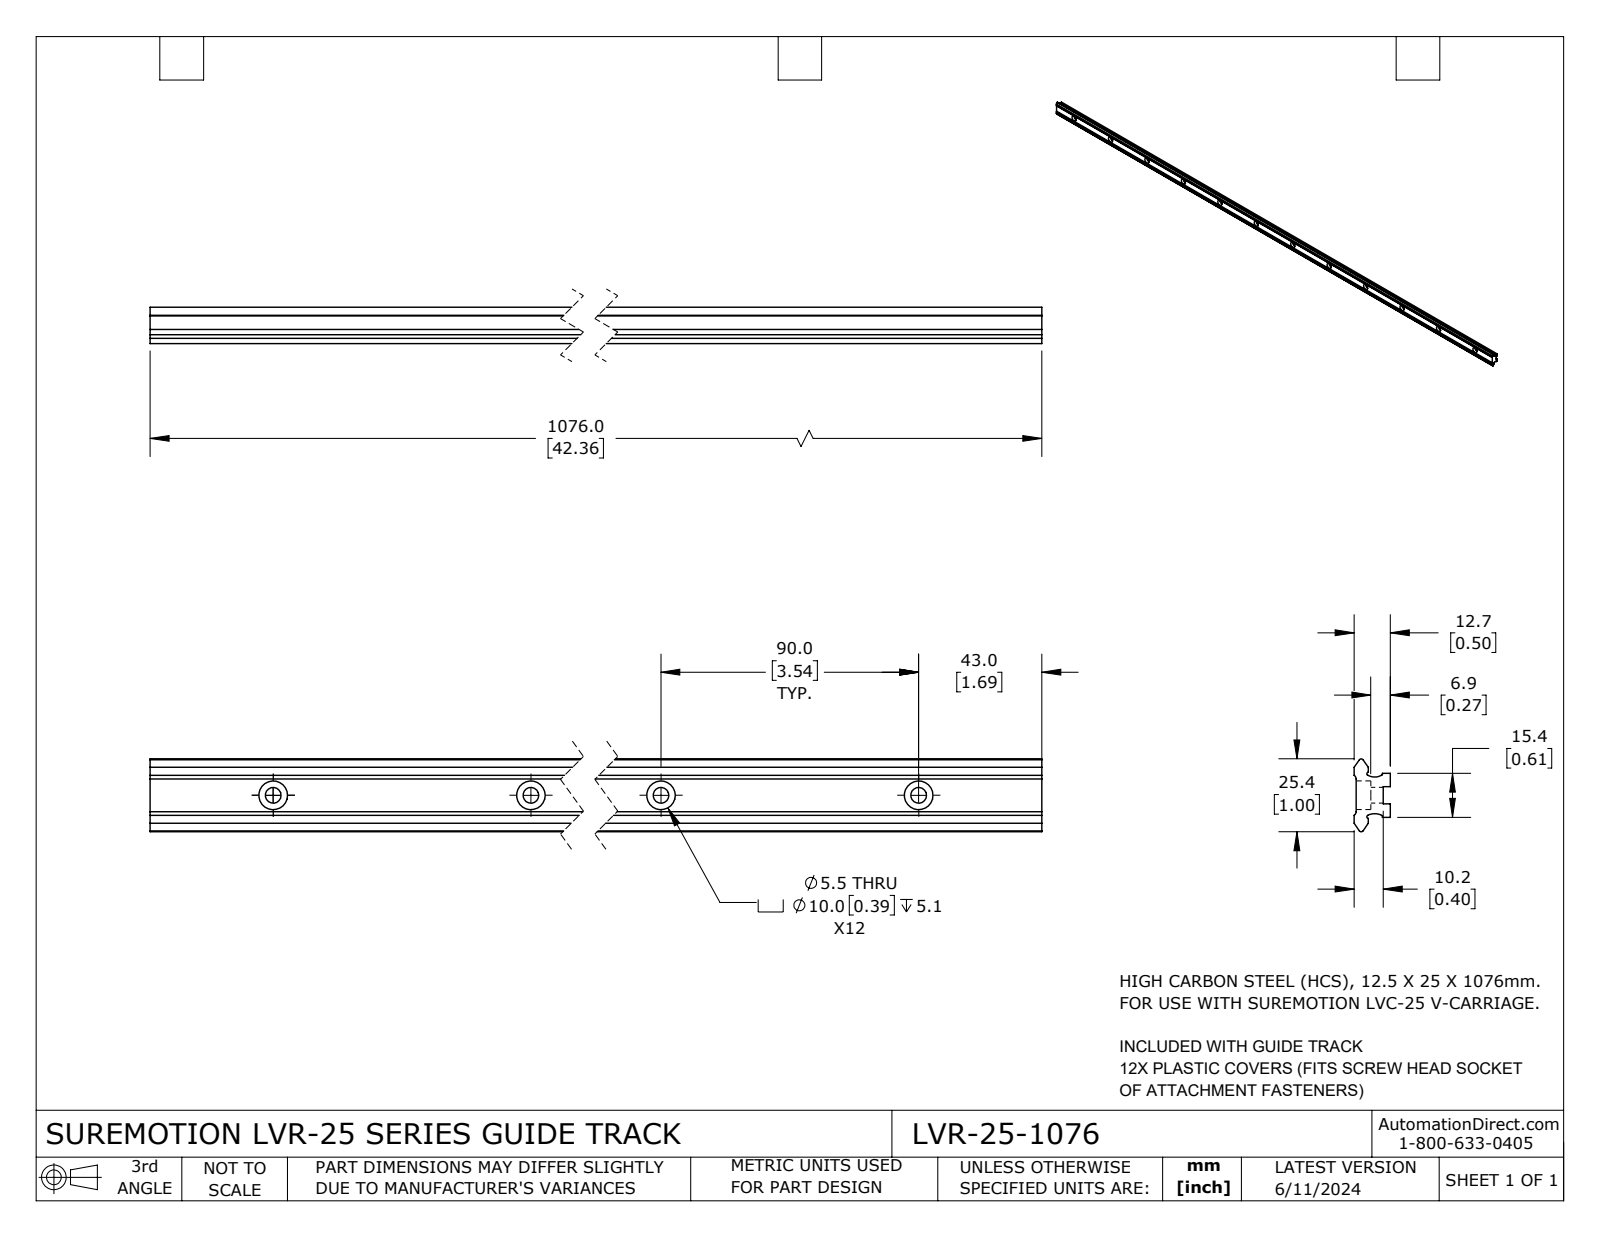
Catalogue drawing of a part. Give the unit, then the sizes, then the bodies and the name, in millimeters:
Units: millimetres
Overall size (bounding box): 1076 × 25.45 × 12.66
Round holes (diameter × count): ⌀5.5 ×12, ⌀10 ×12
Partial cylindrical surfaces — rounded edges, fillets, slot ends (radius × count): R0.55 ×4, R0.76 ×2, R1.5 ×2, R5.22 ×2
Main face-to-face distances: 11.96, 15.25, 2.5, 9.46, 12.66, 10.16, 0.7, 4.7, 10.7, 7.73
Hole centre spacings: 90, 180, 270, 360, 450, 540, 630, 720
Volume: 205 139 mm³ · Surface area: 88 585 mm²
Bodies: 1 solid, 90 faces (30 planar, 60 cylindrical, 0 other)
Part name (STEP PRODUCT): LVR-25-1076
STEP written by: SolidWorks 2023 (CONFIG_CONTROL_DESIGN)
